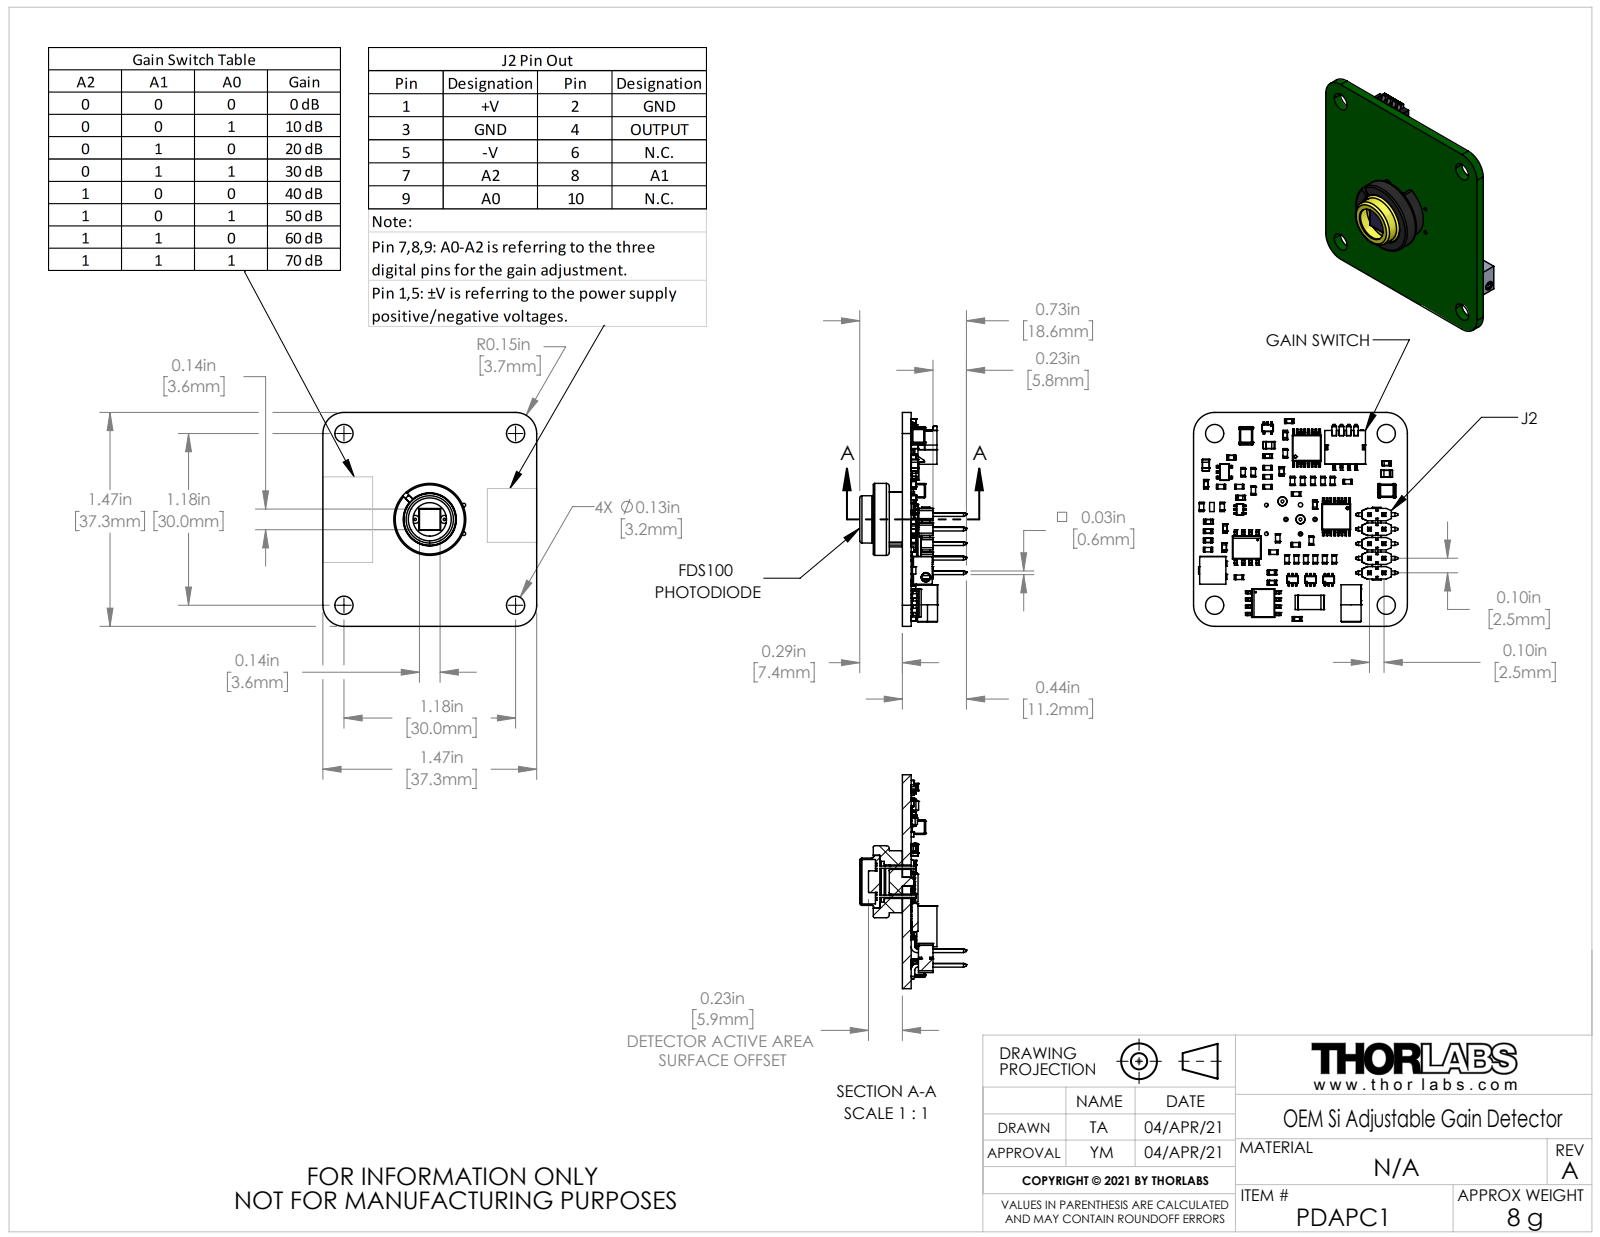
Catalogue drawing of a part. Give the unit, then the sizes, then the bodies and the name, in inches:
Units: inches
Overall size (bounding box): 1.47 × 1.47 × 0.733
Round holes (diameter × count): ⌀0.008 ×5, ⌀0.03 ×4, ⌀0.125 ×4, ⌀0.02 ×2, ⌀0.025 ×2, ⌀0.055 ×2, ⌀0.063 ×2, ⌀0.04 ×1, ⌀0.047 ×1, ⌀0.064 ×1, ⌀0.095 ×1, ⌀0.114 ×1
Round bosses / shafts (diameter × count): ⌀0.06 ×3, ⌀0.016 ×3, ⌀0.495 ×1, ⌀0.36 ×1, ⌀0.325 ×1, ⌀0.138 ×1, ⌀0.089 ×1, ⌀0.04 ×1
Partial cylindrical surfaces — rounded edges, fillets, slot ends (radius × count): R0.004 ×59, R0.008 ×54, R0.01 ×10, R0.02 ×10, R0.005 ×8, R0.014 ×8, R0.01 ×6, R0.145 ×4
Main face-to-face distances: 0.06, 0.1, 0.2, 0.155, 0.219, 1.47, 0.065, 0.215, 0.045, 0.044
Hole centre spacings: 0.1, 0.141, 0.767, 0.908, 1.18, 0.126, 0.167, 0.2
Volume: 0.197 in³ · Surface area: 8.999 in²
Bodies: 75 solids, 4206 faces (2899 planar, 1033 cylindrical, 274 other)
Part name (STEP PRODUCT): TTN235959
STEP written by: SolidWorks 2018 (AUTOMOTIVE_DESIGN)
